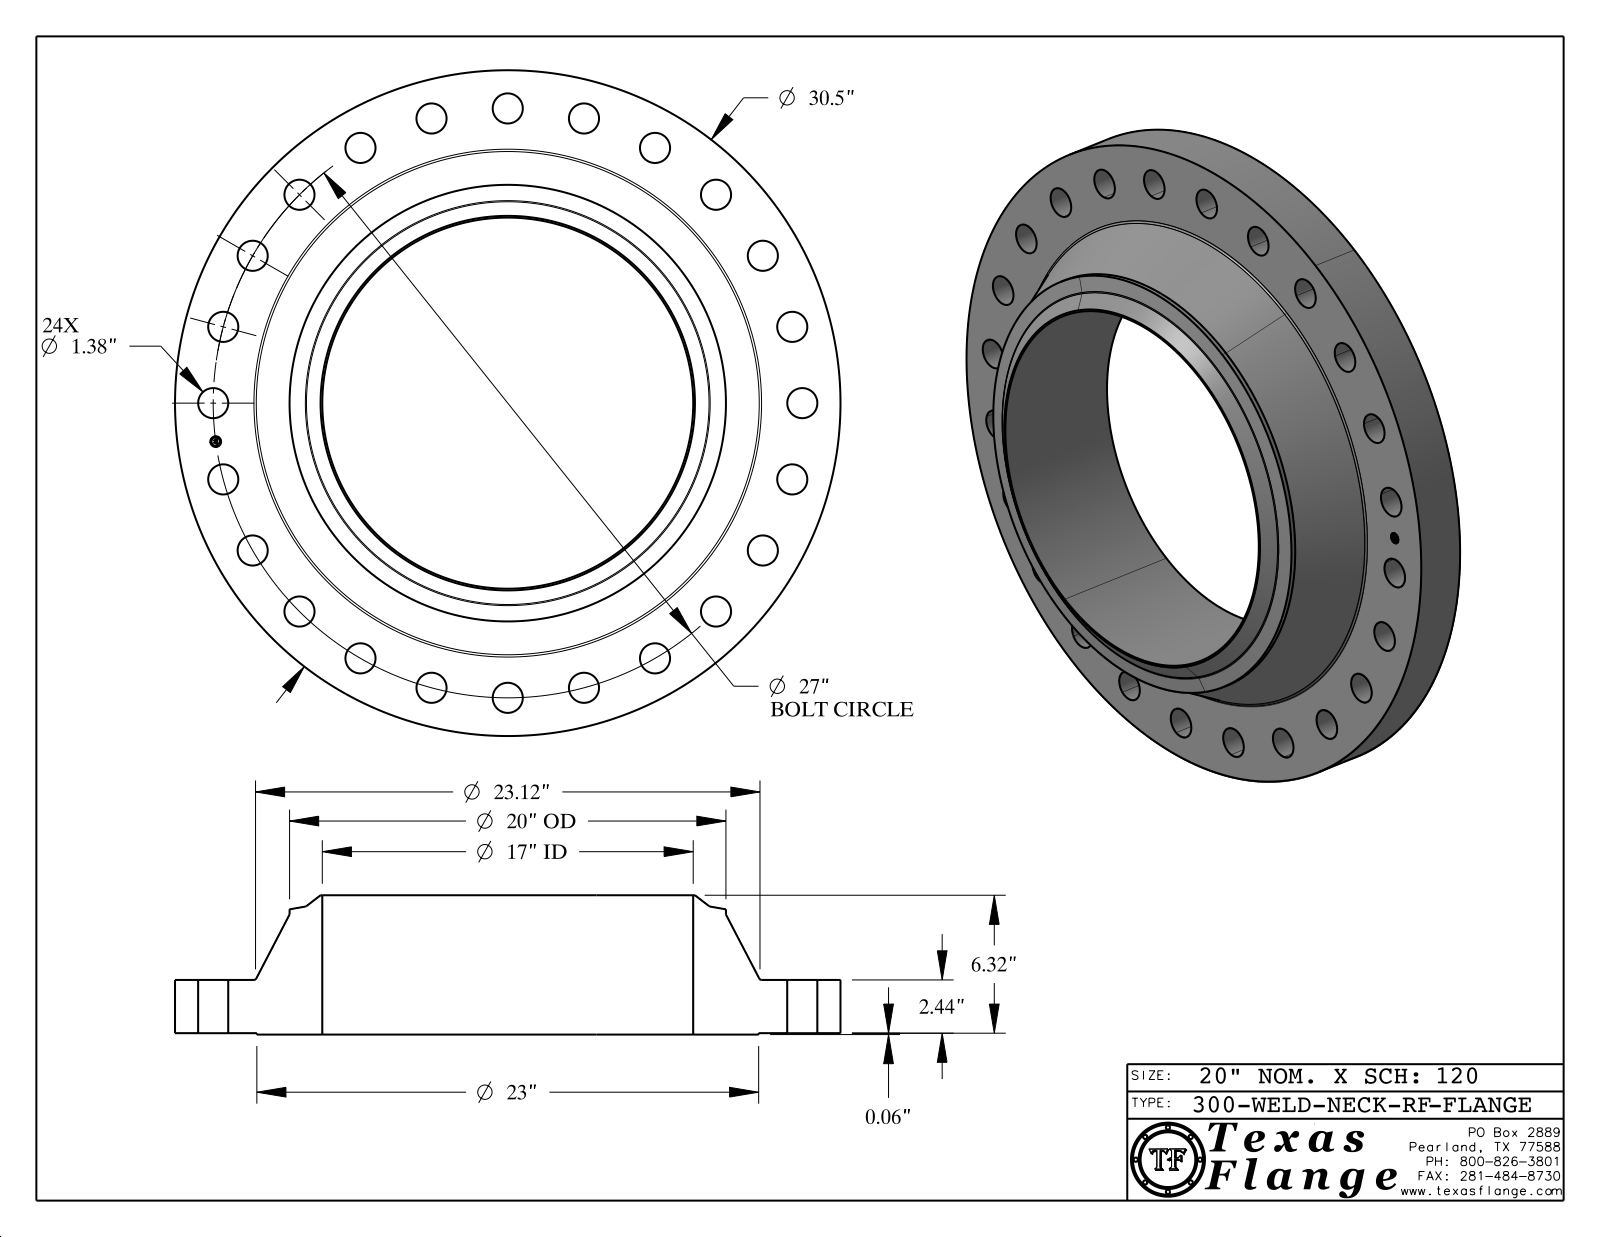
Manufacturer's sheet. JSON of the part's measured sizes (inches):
{"part_name": "300-WELD-NECK-RF", "step_written_by": "CATIA V5 STEP AP214 (AUTOMOTIVE_DESIGN)", "units": "inches", "bodies": {"solids": 1, "faces": 455, "planar": 369, "cylindrical": 76, "other": 10}, "overall_size": [30.5, 30.5, 6.383], "volume_in3": 1610, "surface_area_in2": 1916, "round_holes": [[1.38, 24], [0.495, 1], [17, 1]], "round_bosses_or_shafts": [[0.03, 8], [30.5, 1], [23, 1], [20, 1], [0.39, 1]], "face_to_face_distances": [2.44, 0.063, 2.503, 6.383, 6.32, 3.88, 2.488, 2.425, 0.015, 3.895], "hole_center_spacings": [13.5, 3.524, 6.988, 10.333, 16.437, 24.945, 26.769, 21.421]}
